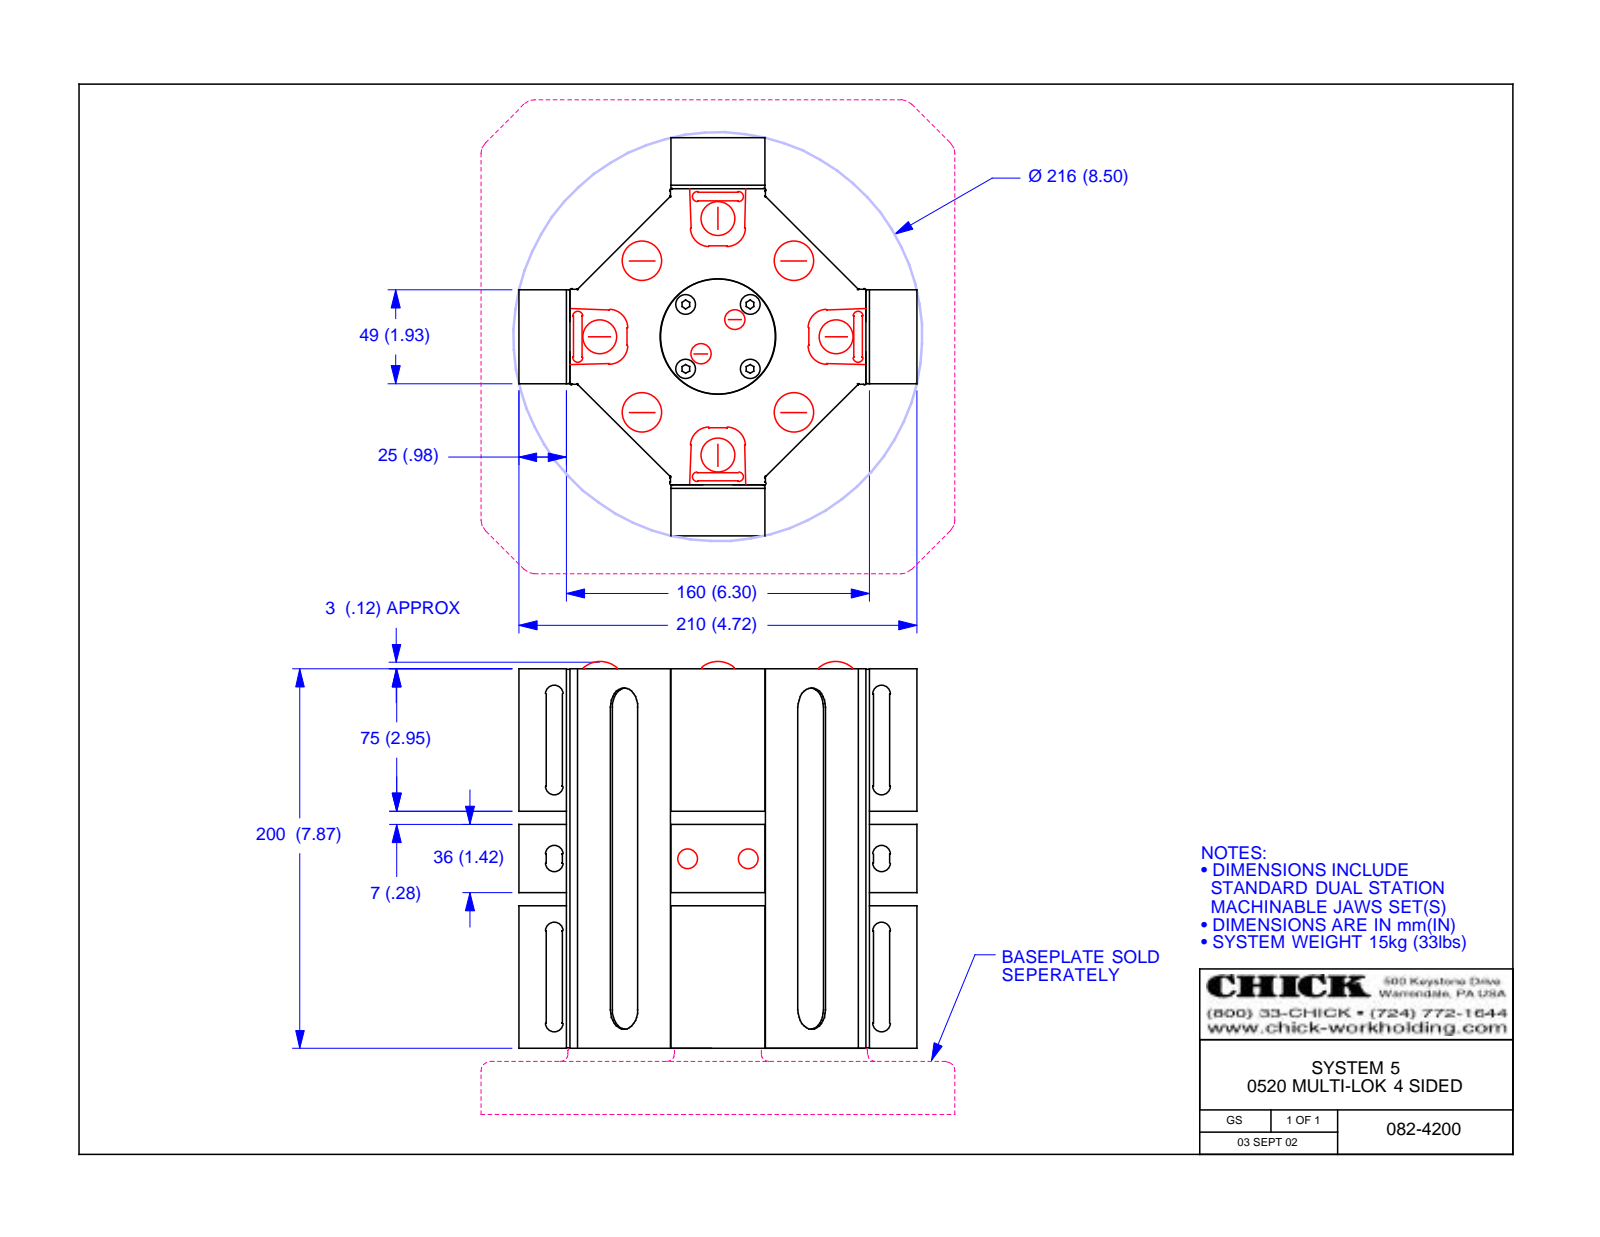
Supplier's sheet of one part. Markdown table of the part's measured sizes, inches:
| quantity | value |
| --- | --- |
| part name | 082-4200; 082-4210; 080-0313-21; 080-2500 (+2 more) |
| STEP written by | Autodesk Inventor 2013 (AUTOMOTIVE_DESIGN) |
| units | inches |
| bodies | 17 solids, 2068 faces (827 planar, 495 cylindrical, 746 other) |
| overall size | 8.268 × 8.268 × 8.031 |
| volume | 235.1 in³ |
| surface area | 746.8 in² |
| round holes (diameter × count) | 0.163 × 12, 0.394 × 12, 0.5 × 12, 0.398 × 8, 0.787 × 8, 0.531 × 5, 0.205 × 4, 0.32 × 4, 0.36 × 4, 0.38 × 4, 0.541 × 4, 0.712 × 4 |
| round bosses / shafts (diameter × count) | 0.551 × 12, 0.604 × 4, 0.375 × 4 |
| partial cylindrical surfaces (radius × count) | 0.031 × 120, 0.039 × 40, 0.094 × 16, 0.075 × 8, 0.13 × 8, 0.223 × 8, 0.311 × 8, 0.437 × 8 |
| main face-to-face distances | 0.079, 6.22, 2.874, 3.426, 2.795, 3.347, 7.205, 7.283, 1.063, 0.984 |
| hole center spacings | 0.096, 0.71, 2.201, 2.589, 2.953, 3.113, 3.21, 3.592 |
